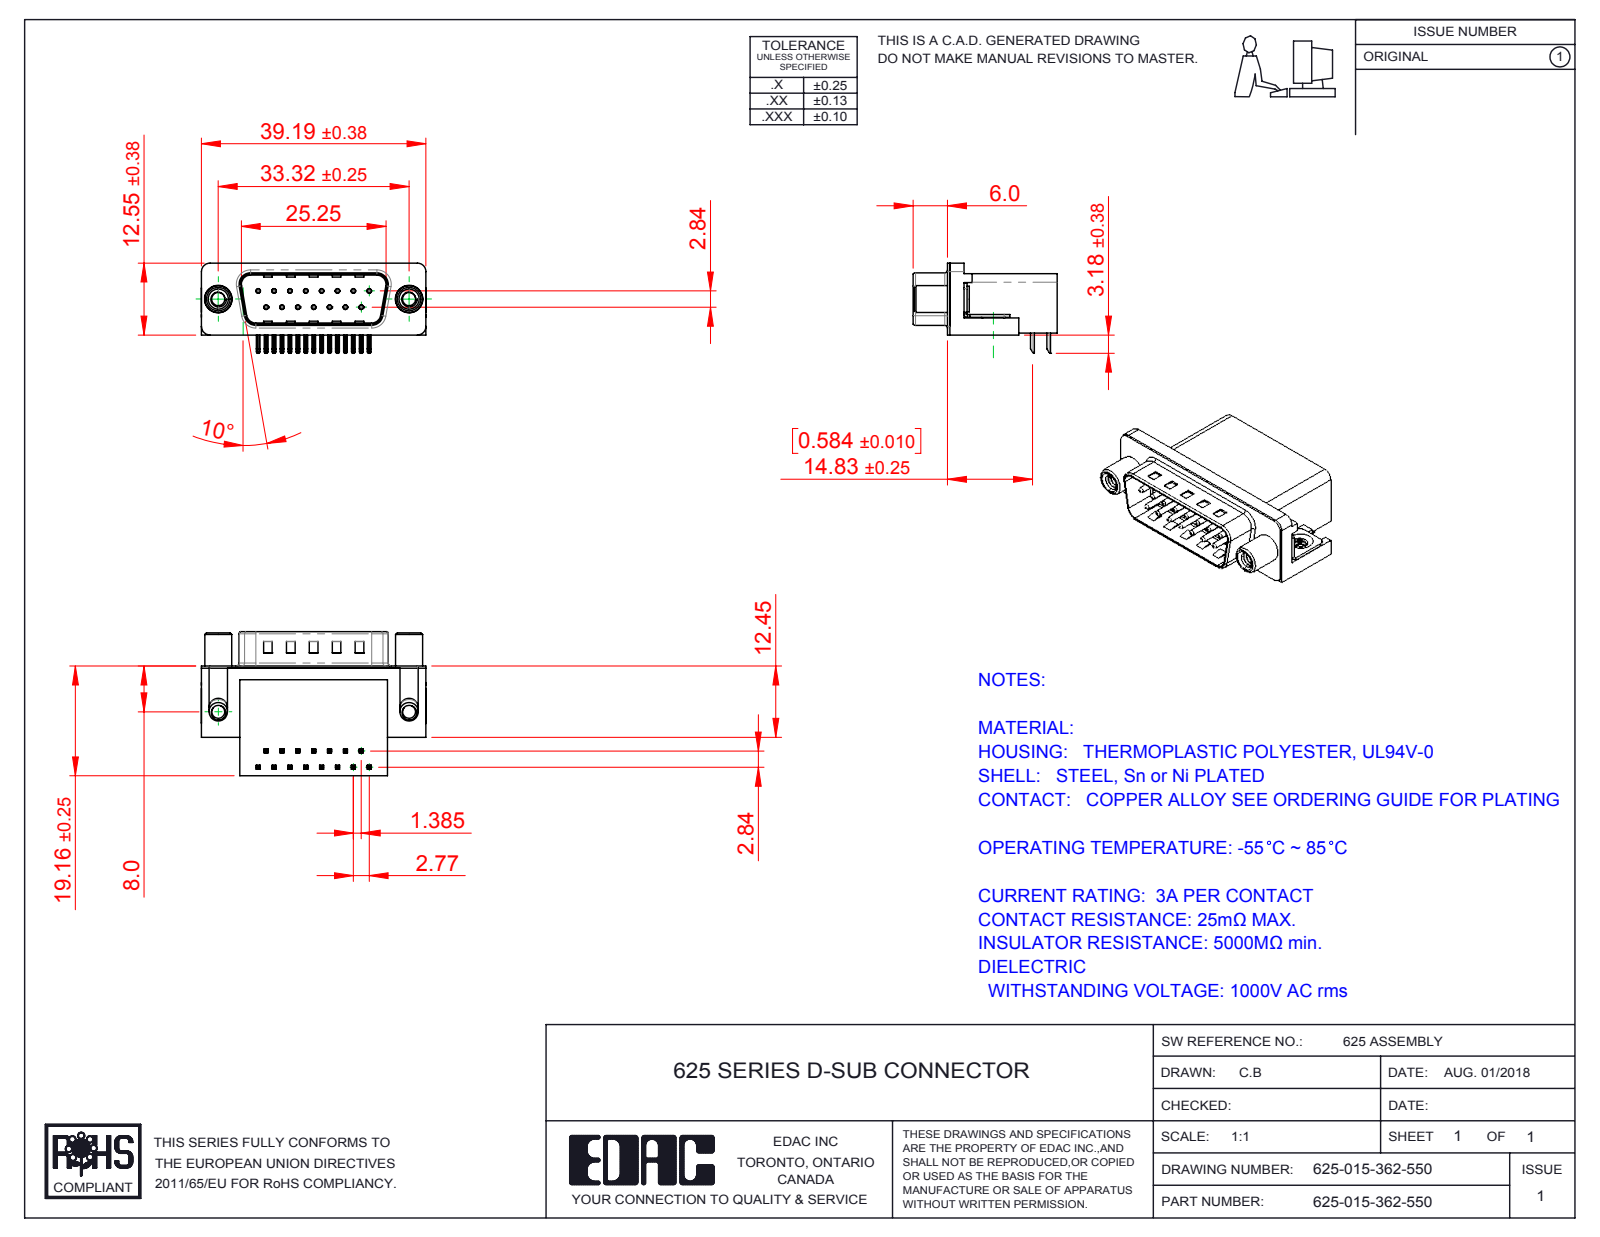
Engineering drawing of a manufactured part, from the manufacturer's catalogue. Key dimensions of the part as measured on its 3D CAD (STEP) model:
Part name (STEP PRODUCT): 625 Housing_15 Socket; 625 Contact Top; 625 4-40 Threaded Board Mount; 625 Shell_15 Socket (+3 more)
STEP written by: SolidWorks 2016 (CONFIG_CONTROL_DESIGN)
Units: millimetres
Bodies: 21 solids, 1505 faces (887 planar, 467 cylindrical, 151 other)
Overall size (bounding box): 39.22 × 25.16 × 15.73
Volume: 6 344 mm³ · Surface area: 6 703 mm²
Round holes (diameter × count): ⌀0.35 ×15, ⌀0.8 ×15, ⌀2.26 ×2, ⌀2.3 ×2, ⌀3.1 ×2, ⌀4 ×2, ⌀4.8 ×2, ⌀5 ×2
Round bosses / shafts (diameter × count): ⌀0.75 ×15, ⌀4.9 ×2, ⌀4.7 ×2, ⌀4.5 ×2, ⌀3.85 ×2, ⌀3.26 ×2
Partial cylindrical surfaces — rounded edges, fillets, slot ends (radius × count): R0.25 ×60, R0.12 ×30, R1 ×16, R0.5 ×9, R1.6 ×8, R1.5 ×6, R0.9 ×4, R2 ×4
Main face-to-face distances: 0.4, 10.35, 18.76, 2.1, 10.46, 1.7, 10.86, 19.16, 8.76, 16.26
Hole centre spacings: 3.16, 2.77, 5.54, 8.31, 11.08, 5.03, 5.04, 7.48
